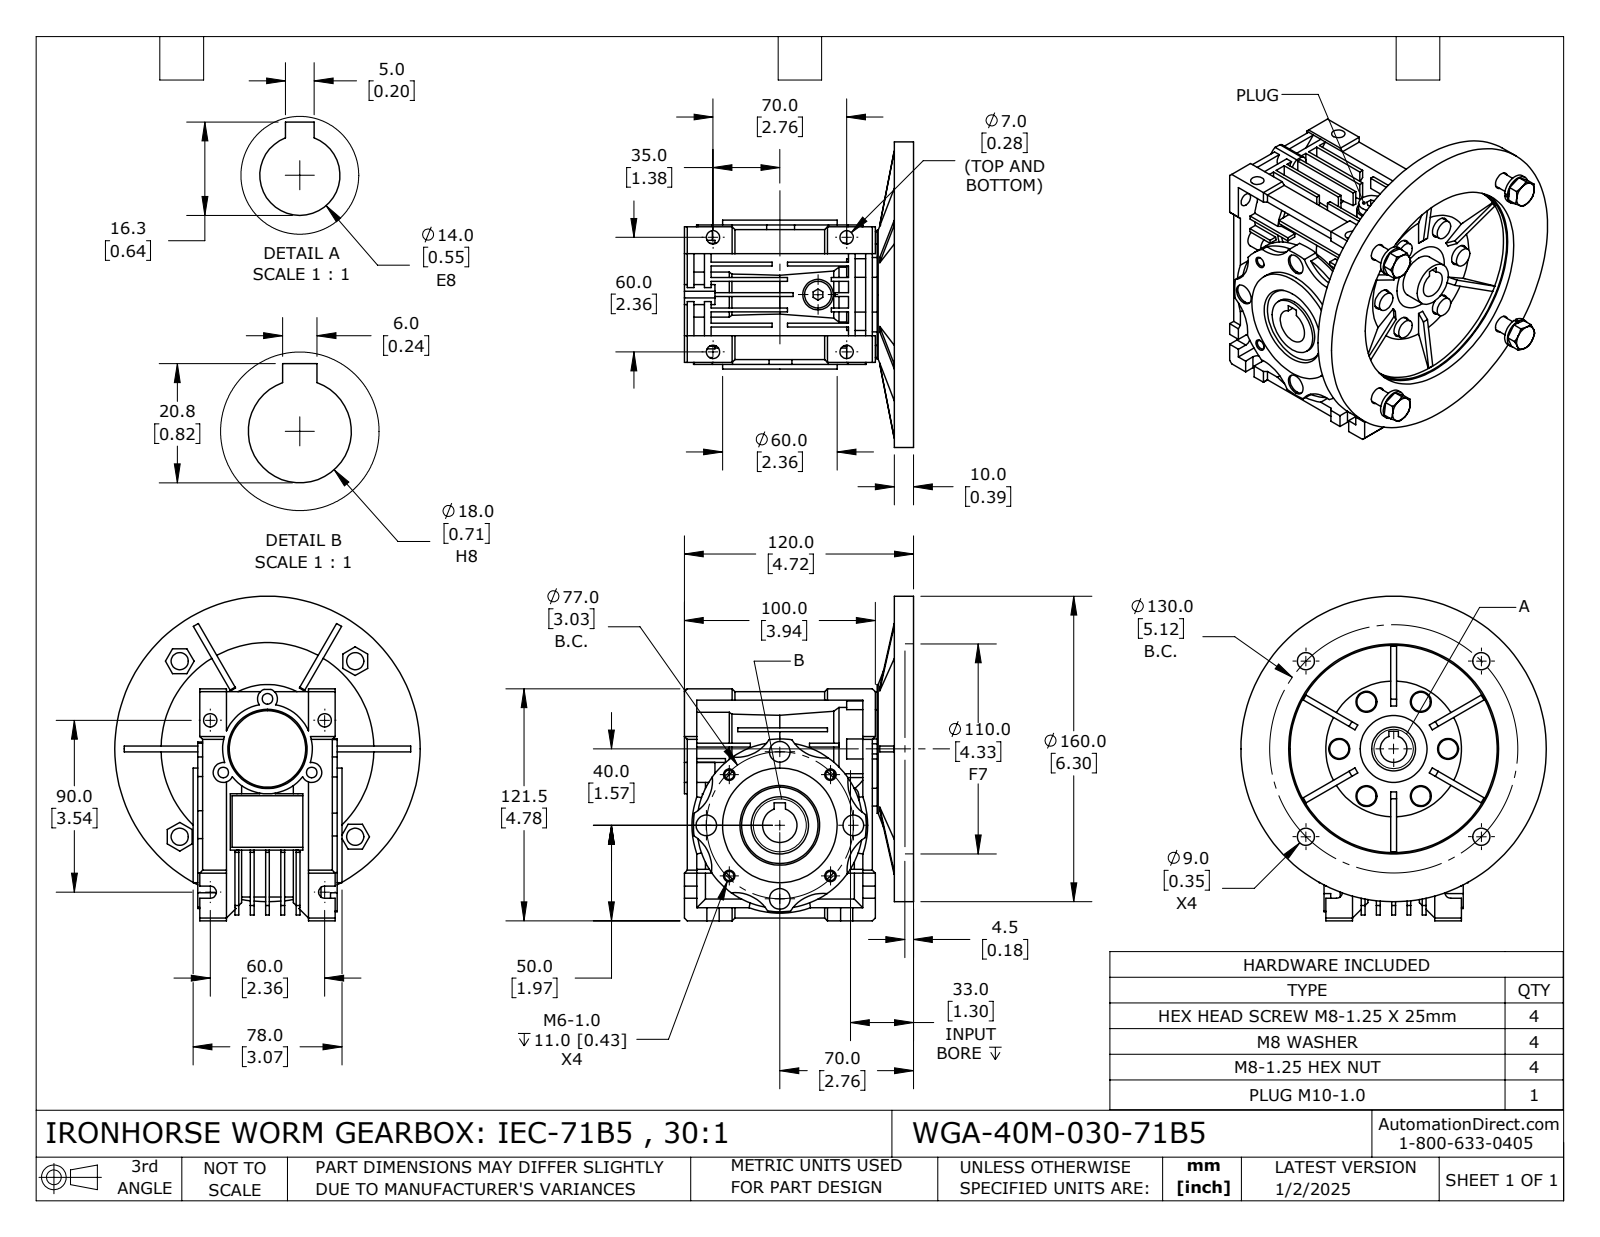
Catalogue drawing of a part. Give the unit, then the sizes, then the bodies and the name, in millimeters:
Units: millimetres
Overall size (bounding box): 170 × 160 × 137.68
Round holes (diameter × count): ⌀7 ×6, ⌀11 ×6, ⌀9 ×5, ⌀4.92 ×4, ⌀6.8 ×4, ⌀8 ×4, ⌀8.2 ×4, ⌀10.8 ×4, ⌀5.55 ×3, ⌀14 ×1, ⌀15 ×1, ⌀18 ×1
Round bosses / shafts (diameter × count): ⌀10 ×6, ⌀15.4 ×4, ⌀160 ×1, ⌀75 ×1, ⌀67.5 ×1, ⌀60 ×1, ⌀54 ×1, ⌀47 ×1
Partial cylindrical surfaces — rounded edges, fillets, slot ends (radius × count): R20 ×8, R3.2 ×6, R5.22 ×6, R5.25 ×3, R43.5 ×1, R43.59 ×1, R45.25 ×1, R46 ×1
Main face-to-face distances: 10, 8, 2, 6, 5, 1.5, 16, 24, 14, 2.5
Hole centre spacings: 28.5, 29.1, 70.22, 49.36, 33.54, 37.5, 38.19, 38.5
Volume: 780 077 mm³ · Surface area: 202 021 mm²
Bodies: 18 solids, 1101 faces (630 planar, 290 cylindrical, 181 other)
Part name (STEP PRODUCT): WGA-40M-030-71B5
STEP written by: SolidWorks 2024 (CONFIG_CONTROL_DESIGN)
